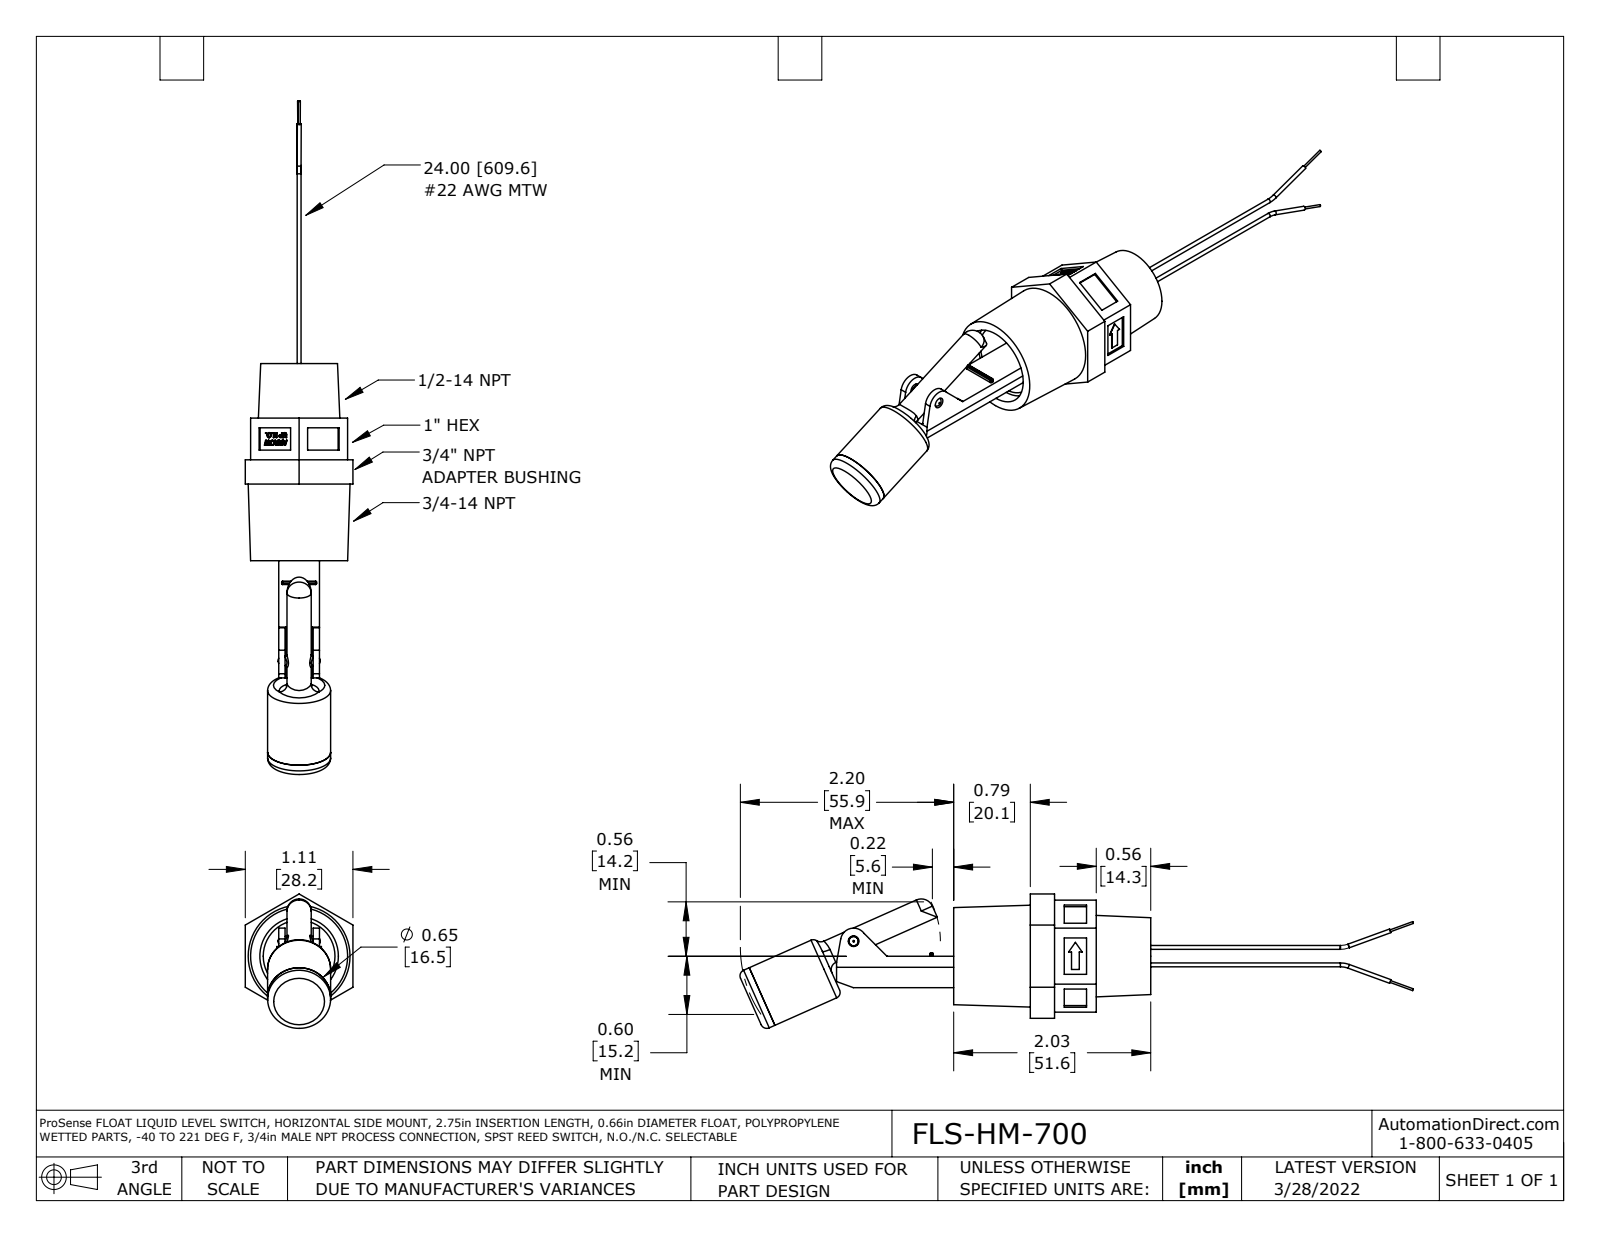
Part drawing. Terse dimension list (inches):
name: ADM8700-C nc coord r1 fxt
written by: SolidWorks 2017 (AUTOMOTIVE_DESIGN)
unit: in
bodies: 9 solids, 542 faces (305 planar, 71 cylindrical, 166 other)
size: 6.944 × 1.385 × 1.11
volume: 1.613 in³; area: 27.45 in²
holes: 2× ⌀0.01, 2× ⌀0.53, 1× ⌀0.11, 1× ⌀0.45, 1× ⌀0.5, 1× ⌀0.56, 1× ⌀0.7, 1× ⌀0.81
bosses: 4× ⌀0.04, 2× ⌀0.65, 2× ⌀0.02, 1× ⌀0.55, 1× ⌀0.25, 1× ⌀0.125
rounds: 9× R0.01, 4× R0.009, 2× R0.02, 1× R0.1, 1× R0.105, 1× R0.125, 1× R0.135, 1× R0.21
face distances: 0.055, 1.055, 0.43, 0.075, 0.992, 1, 1.11, 1.035, 0.02, 0.98
hole spacings: 0.09, 0.18
